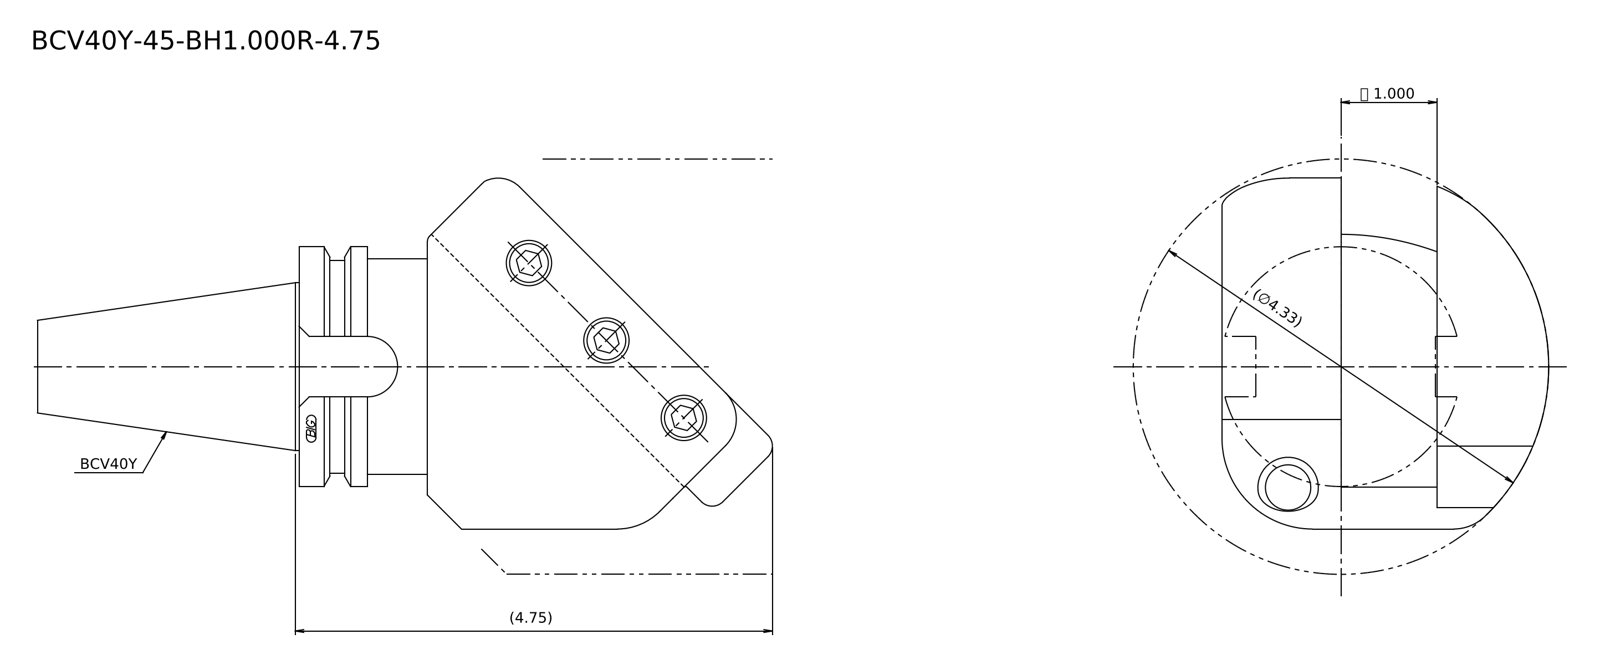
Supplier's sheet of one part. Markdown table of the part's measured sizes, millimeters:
| quantity | value |
| --- | --- |
| STEP written by | Kubotek KeyCreator 2011 V10.0.2 (22737) (automotive_design) |
| units | millimeters |
| bodies | 1 solid, 29 faces (16 planar, 9 cylindrical, 4 other) |
| overall size | 196.25 × 96 × 86.75 |
| volume | 508 909 mm³ |
| surface area | 49 792 mm² |
| round bosses / shafts (diameter × count) | 63.5 × 1, 57 × 1, 56.36 × 1, 44.45 × 1 |
| partial cylindrical surfaces (radius × count) | 12 × 1, 24 × 1, 55 × 1 |
| main face-to-face distances | 25.4, 56.9, 31.5, 34, 15.95, 18.05, 10, 103.25, 87.3, 69.25 |
